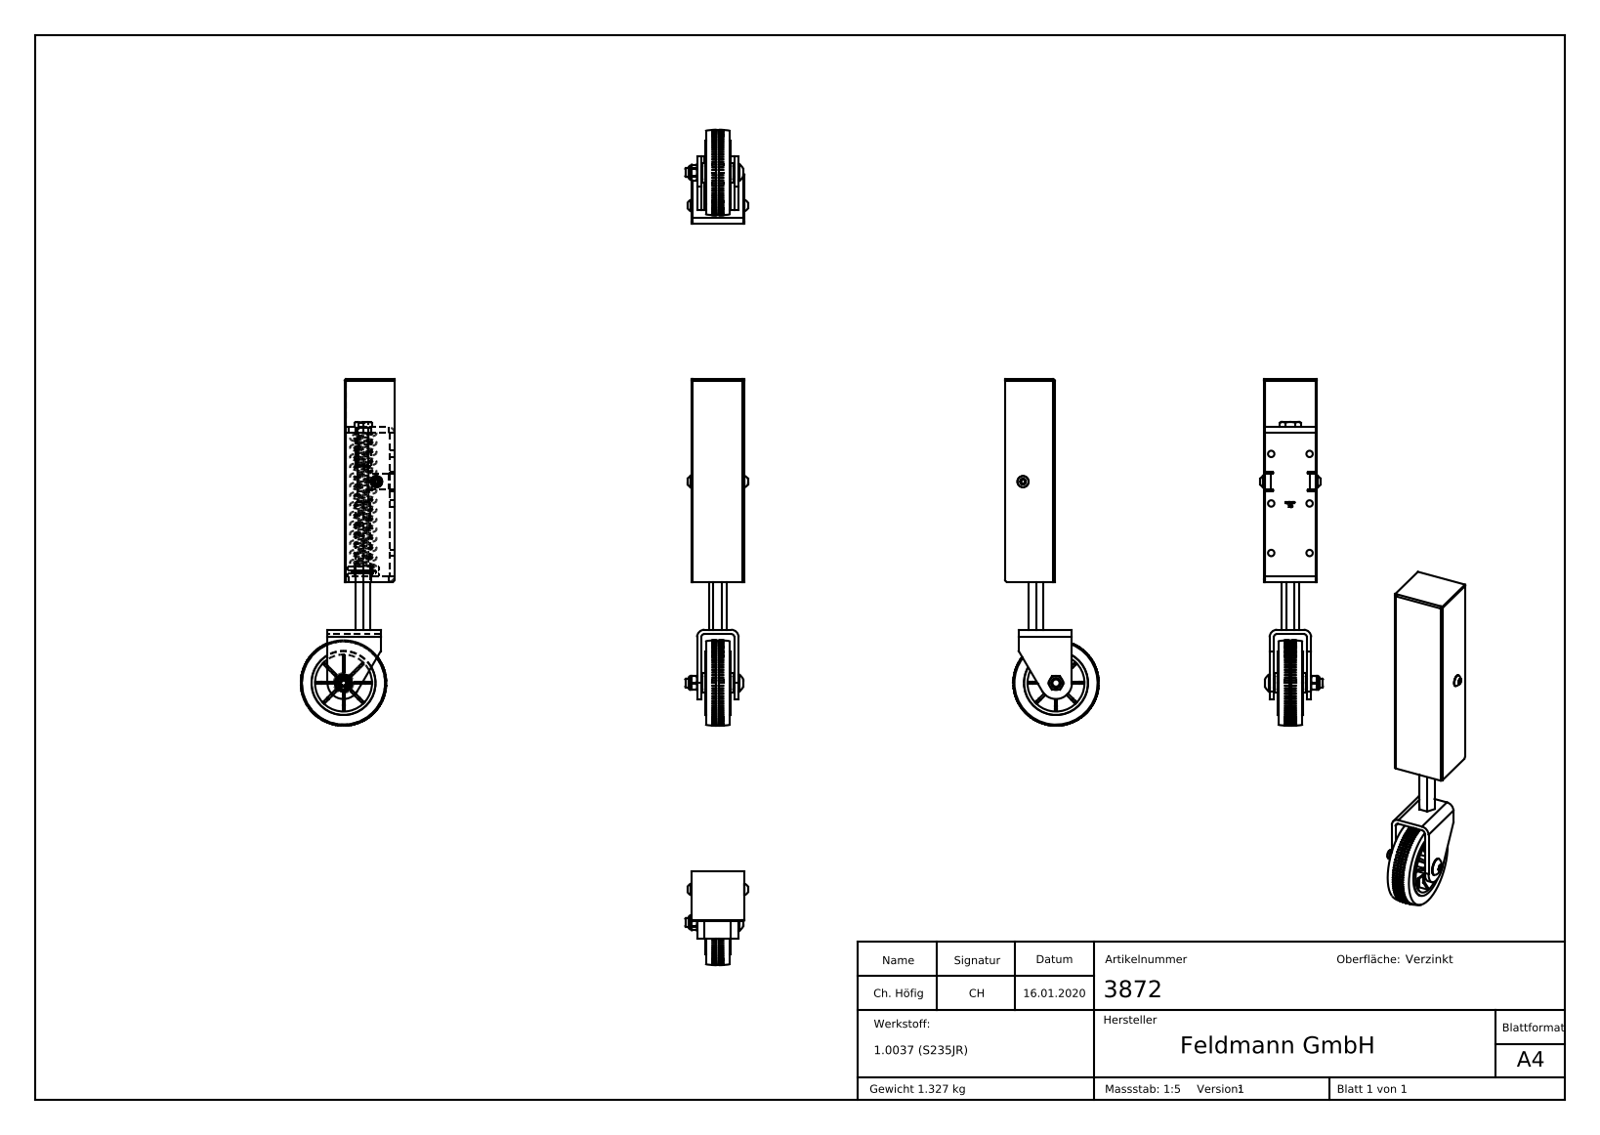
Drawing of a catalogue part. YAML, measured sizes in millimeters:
part_name: "DIN 7380_DIN 7380 M8x50; 3872 Teil5_3872 Teil5; 3872 Teil8_3872 Teil8; 3872 Teil4 (+8 more)"
step_written_by: "SolidWorks 2015 (CONFIG_CONTROL_DESIGN)"
units: millimeters
bodies: {solids: 17, faces: 1825, planar: 1216, cylindrical: 158, other: 451}
overall_size: [15302.2, 8507.93, 8356.64]
volume: 237211
surface_area: 164390
round_holes:
  - {diameter: 6, count: 6}
  - {diameter: 5, count: 1}
  - {diameter: 6.4, count: 1}
  - {diameter: 6.8, count: 1}
  - {diameter: 8.5, count: 1}
  - {diameter: 8.7, count: 1}
  - {diameter: 8.8, count: 1}
  - {diameter: 12, count: 1}
  - {diameter: 12.8, count: 1}
  - {diameter: 17, count: 1}
  - {diameter: 17.1, count: 1}
  - {diameter: 53.5, count: 1}
round_bosses_or_shafts:
  - {diameter: 80, count: 1}
  - {diameter: 60, count: 1}
  - {diameter: 30, count: 1}
  - {diameter: 23.4, count: 1}
  - {diameter: 18.3, count: 1}
  - {diameter: 16, count: 1}
  - {diameter: 14, count: 1}
  - {diameter: 13, count: 1}
partial_cylinders:
  - {radius: 0.1, count: 24}
  - {radius: 1.59, count: 16}
  - {radius: 0.5, count: 13}
  - {radius: 0.75, count: 4}
  - {radius: 1.39, count: 4}
  - {radius: 3, count: 4}
  - {radius: 5.5, count: 4}
  - {radius: 1.5, count: 3}
face_to_face_distances: [1, 49, 50, 5, 48, 4, 47, 17.5, 46, 41]
hole_center_spacings: [46.5, 58.81, 36, 93, 99.72, 191.52]
